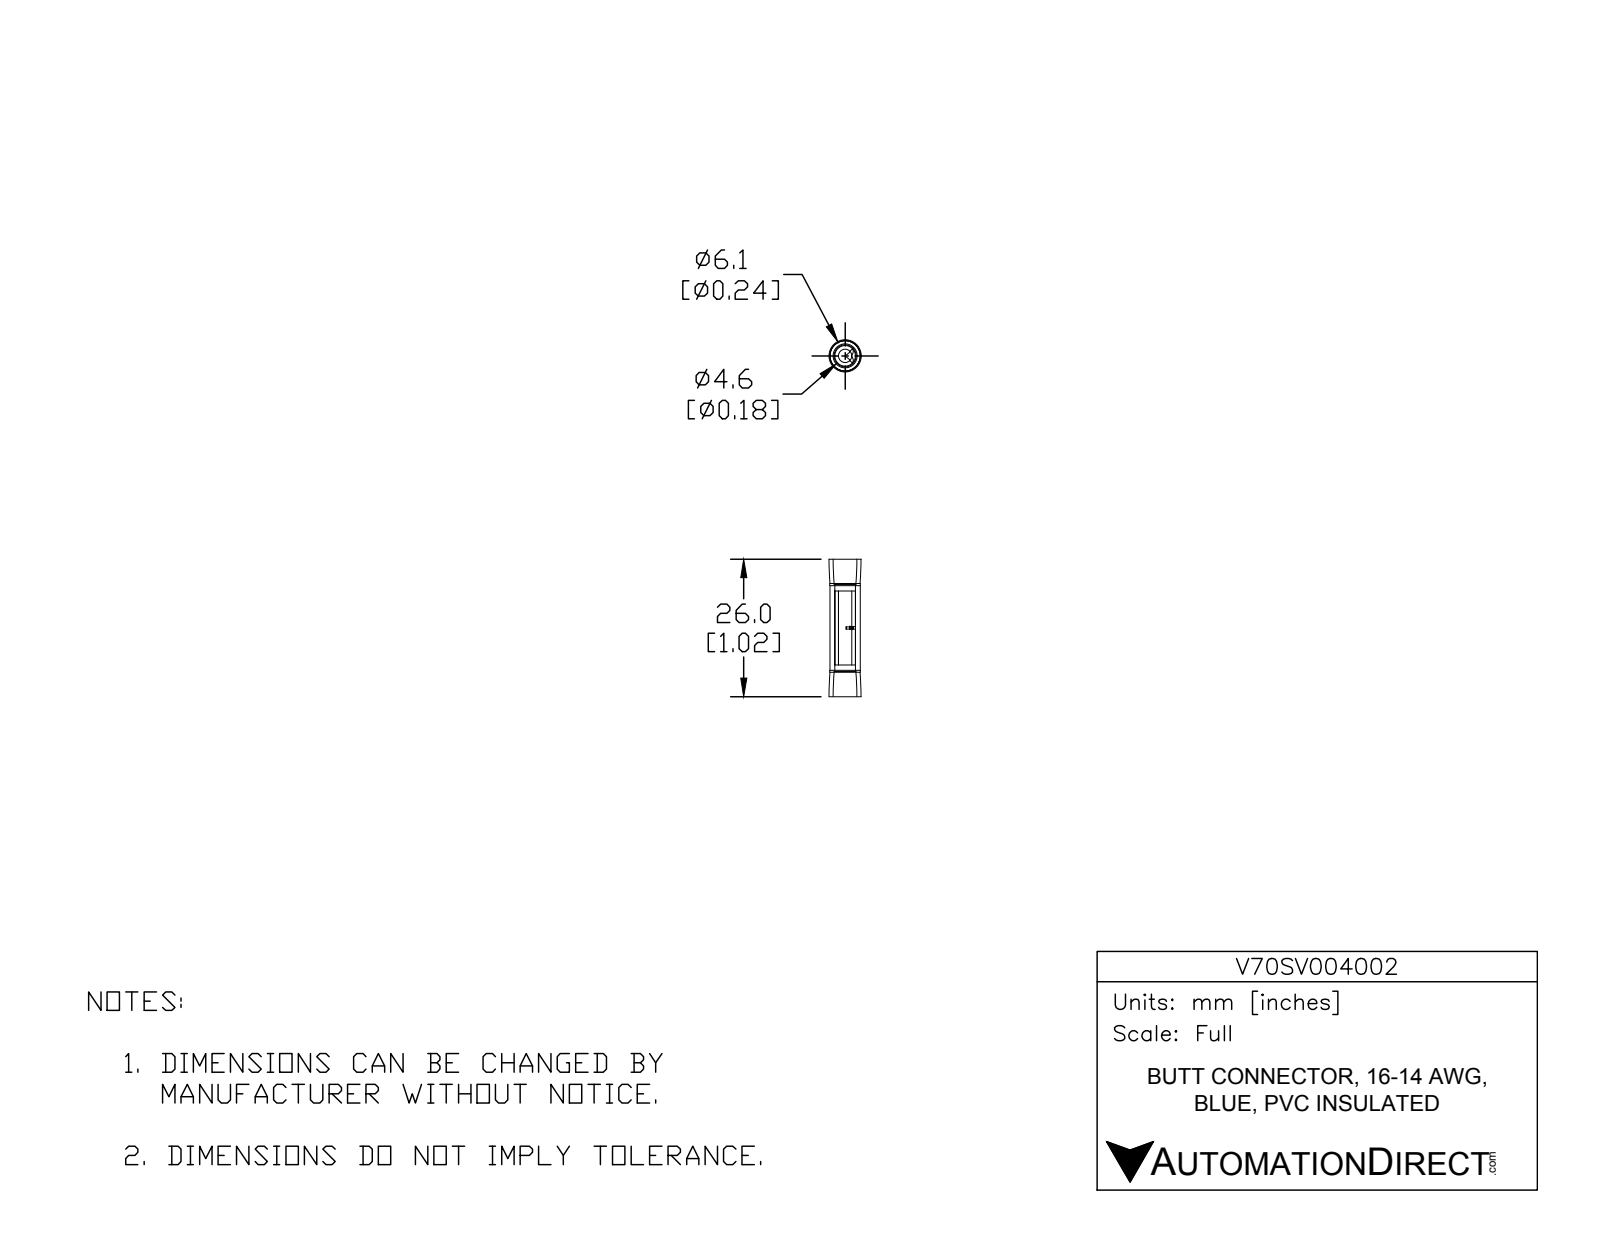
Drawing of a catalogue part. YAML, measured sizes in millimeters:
part_name: "V70SV004002"
step_written_by: "SolidWorks 2017 (AUTOMOTIVE_DESIGN)"
units: millimeters
bodies: {solids: 2, faces: 43, planar: 18, cylindrical: 13, other: 12}
overall_size: [26, 6.1, 6.1]
volume: 442
surface_area: 1159
round_holes:
  - {diameter: 2.5, count: 1}
  - {diameter: 3.9, count: 1}
round_bosses_or_shafts:
  - {diameter: 5.7, count: 1}
partial_cylinders:
  - {radius: 0.1, count: 2}
  - {radius: 0.25, count: 2}
  - {radius: 0.91, count: 2}
face_to_face_distances: [6, 20, 26, 14, 12.8, 13.2, 6.8, 7.2, 12.77, 13.23]
